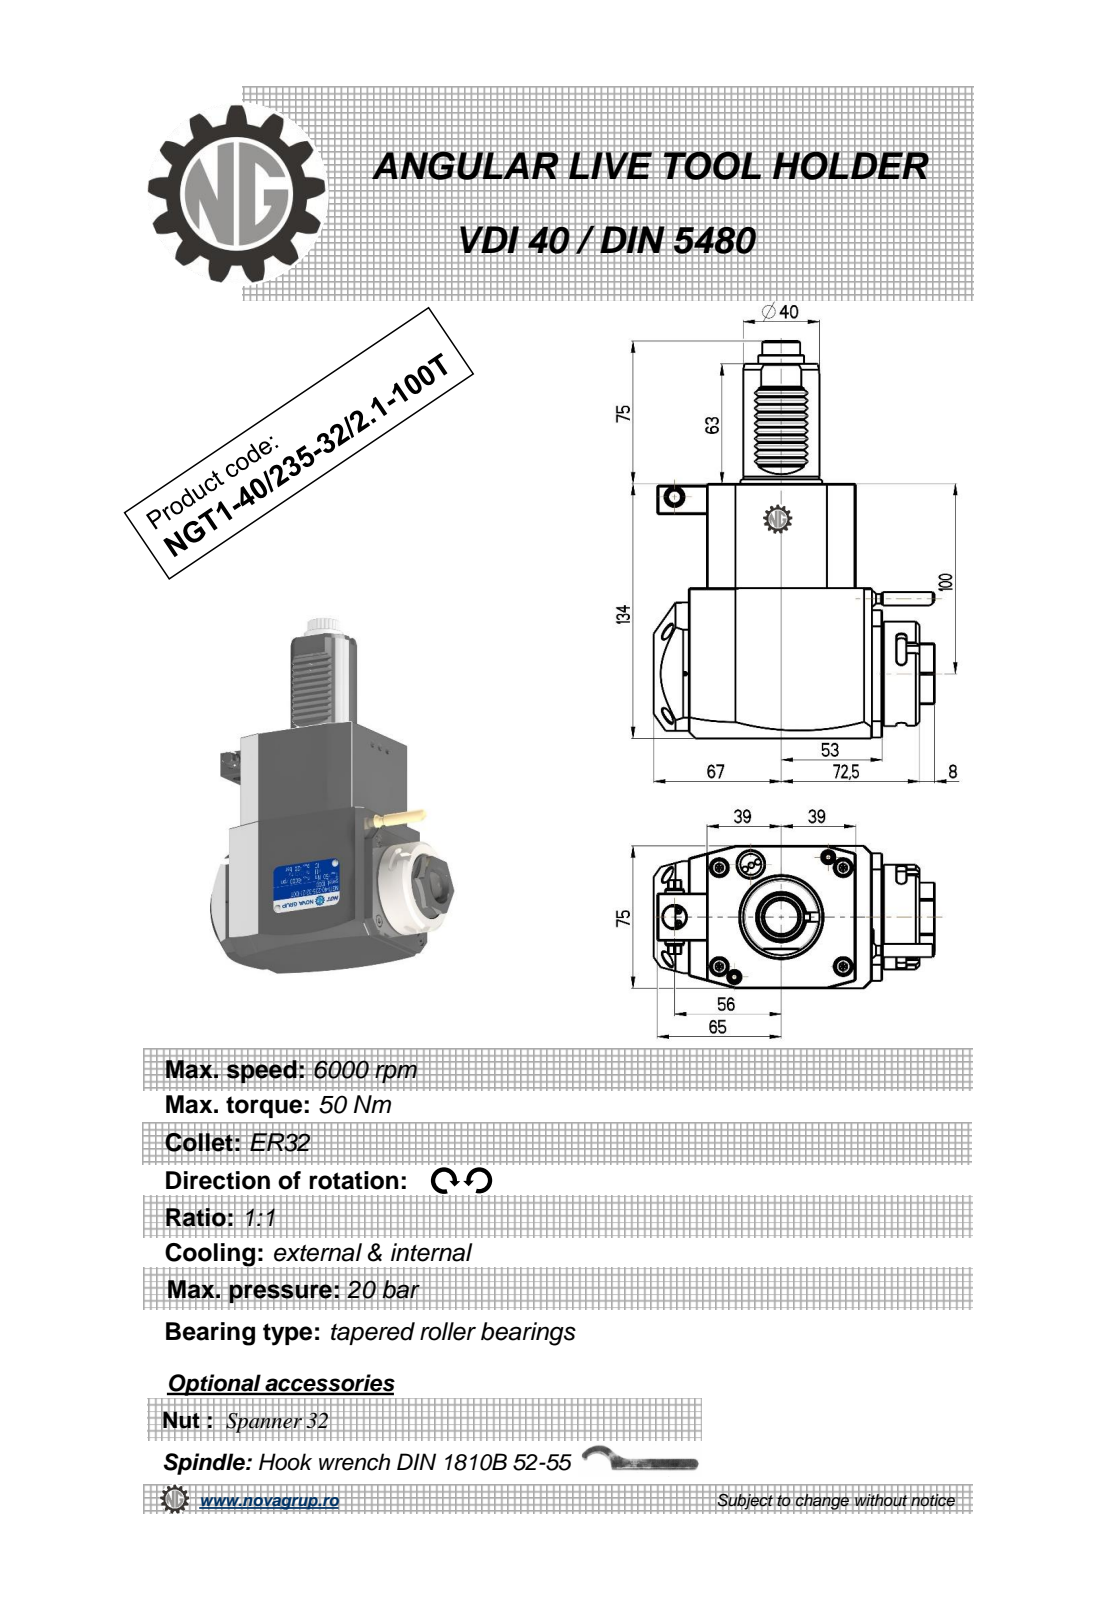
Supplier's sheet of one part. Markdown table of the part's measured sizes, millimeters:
| quantity | value |
| --- | --- |
| part name | NGT1_40_235_32_1_1_100T |
| STEP written by | PRO/ENGINEER BY PARAMETRIC TECHNOLOGY CORPORATION, 2010280 (CONFIG_CONTROL_DESIGN) |
| units | millimeters |
| bodies | 1 solid, 458 faces (192 planar, 172 cylindrical, 94 other) |
| overall size | 209 × 147.5 × 75 |
| volume | 1 080 000 mm³ |
| surface area | 77 887 mm² |
| round holes (diameter × count) | 2.5 × 1, 3 × 1, 9.5 × 1, 12 × 1, 23 × 1 |
| round bosses / shafts (diameter × count) | 8 × 2, 55 × 1, 48 × 1, 40 × 1, 24 × 1, 10 × 1, 7 × 1, 5 × 1 |
| partial cylindrical surfaces (radius × count) | 2.08 × 48, 0.3 × 10, 2.5 × 6, 180 × 2, 3.85 × 1, 4.25 × 1, 9.08 × 1, 9.92 × 1 |
| main face-to-face distances | 75, 134, 78, 14, 92, 79, 25, 84.88, 19.5, 111.5 |
| hole center spacings | 43.2, 54.87, 91.5 |
